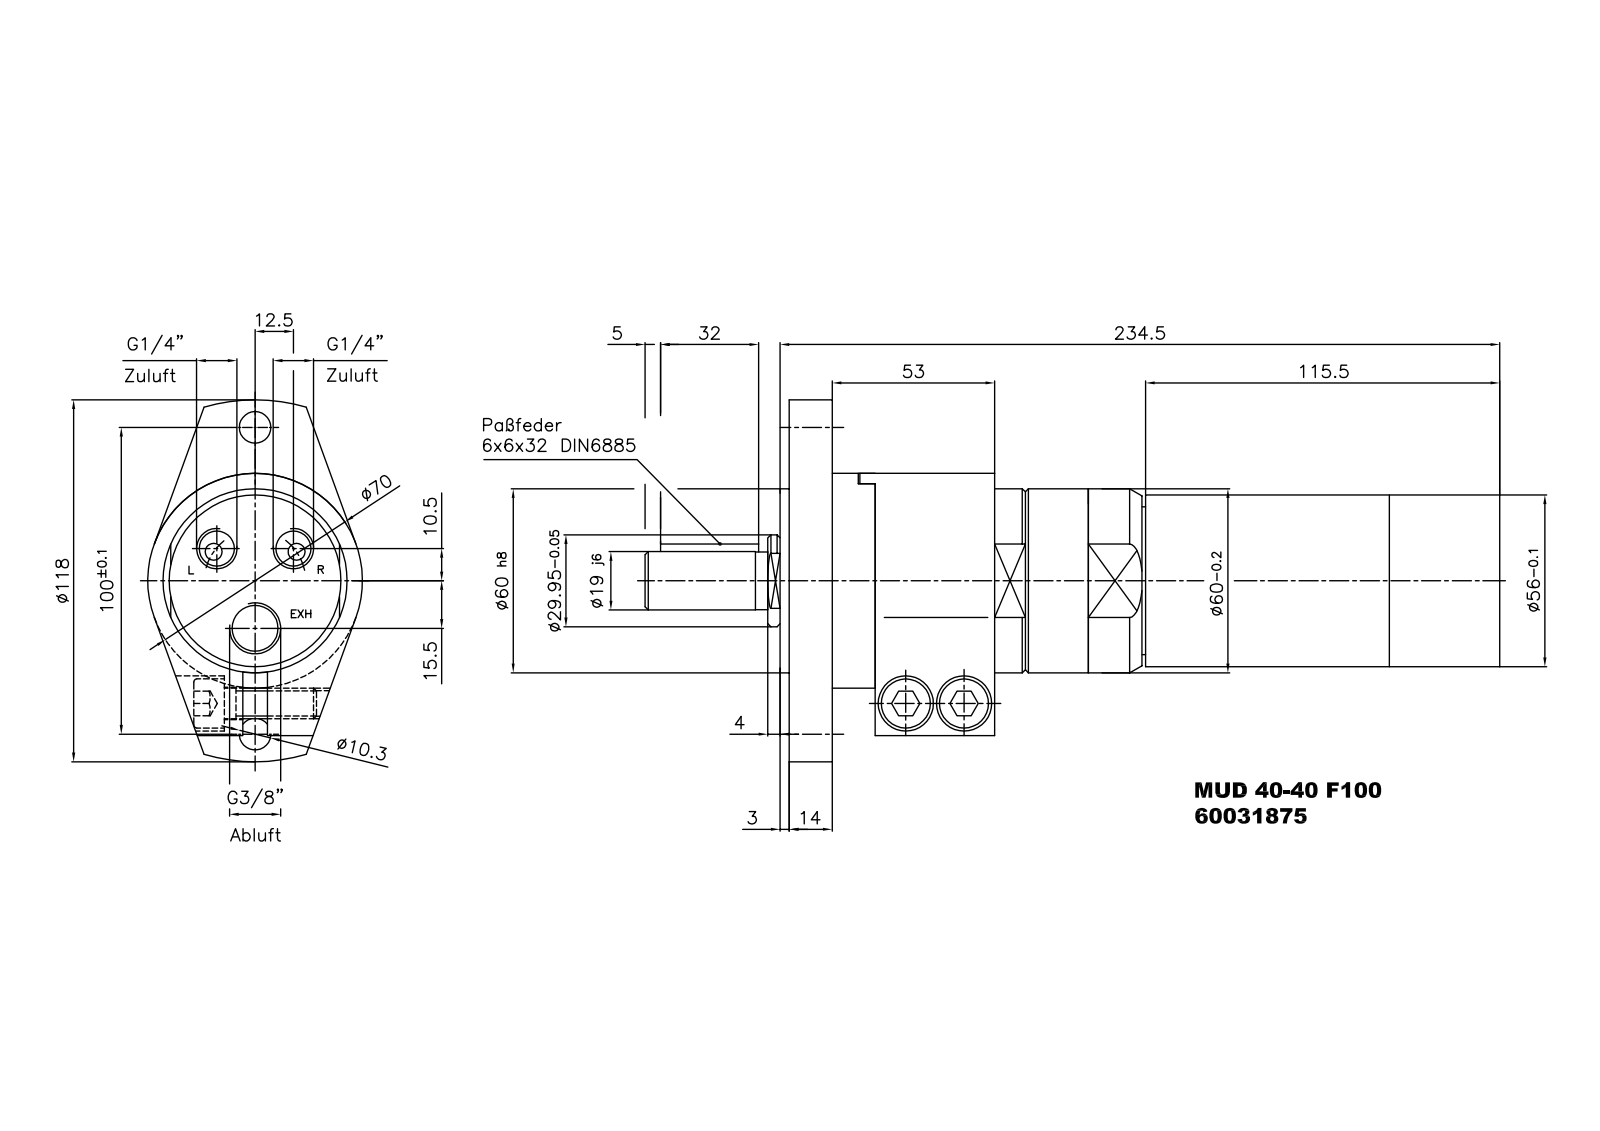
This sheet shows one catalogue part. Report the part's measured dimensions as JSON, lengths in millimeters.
{"part_name": "MUD 40-40 F100_60031875", "step_written_by": "Autodesk Inventor 2016 (AUTOMOTIVE_DESIGN)", "units": "millimeters", "bodies": {"solids": 1, "faces": 169, "planar": 81, "cylindrical": 52, "other": 36}, "overall_size": [278.7, 118, 70], "volume_mm3": 748132, "surface_area_mm2": 80208, "round_holes": [[8.38, 2], [10.3, 2], [10.5, 2], [11.45, 2], [18, 2], [1.55, 1], [1.6, 1], [3, 1], [4, 1], [5.5, 1], [14.95, 1], [18.92, 1]], "round_bosses_or_shafts": [[16, 2], [10, 2], [70, 1], [60, 1], [56, 1], [55.18, 1], [49.73, 1], [29.95, 1]], "partial_cylinders_radius": [[3, 2], [6, 2], [11, 1], [23, 1], [27.28, 1], [59, 1]], "face_to_face_distances": [14, 231.7, 217.7, 17, 3, 234.7, 70.1, 67.1, 53.1, 164.6], "hole_center_spacings": [13.87, 16.32, 28.85, 41.43, 50, 61.78, 15.5, 16.5]}
